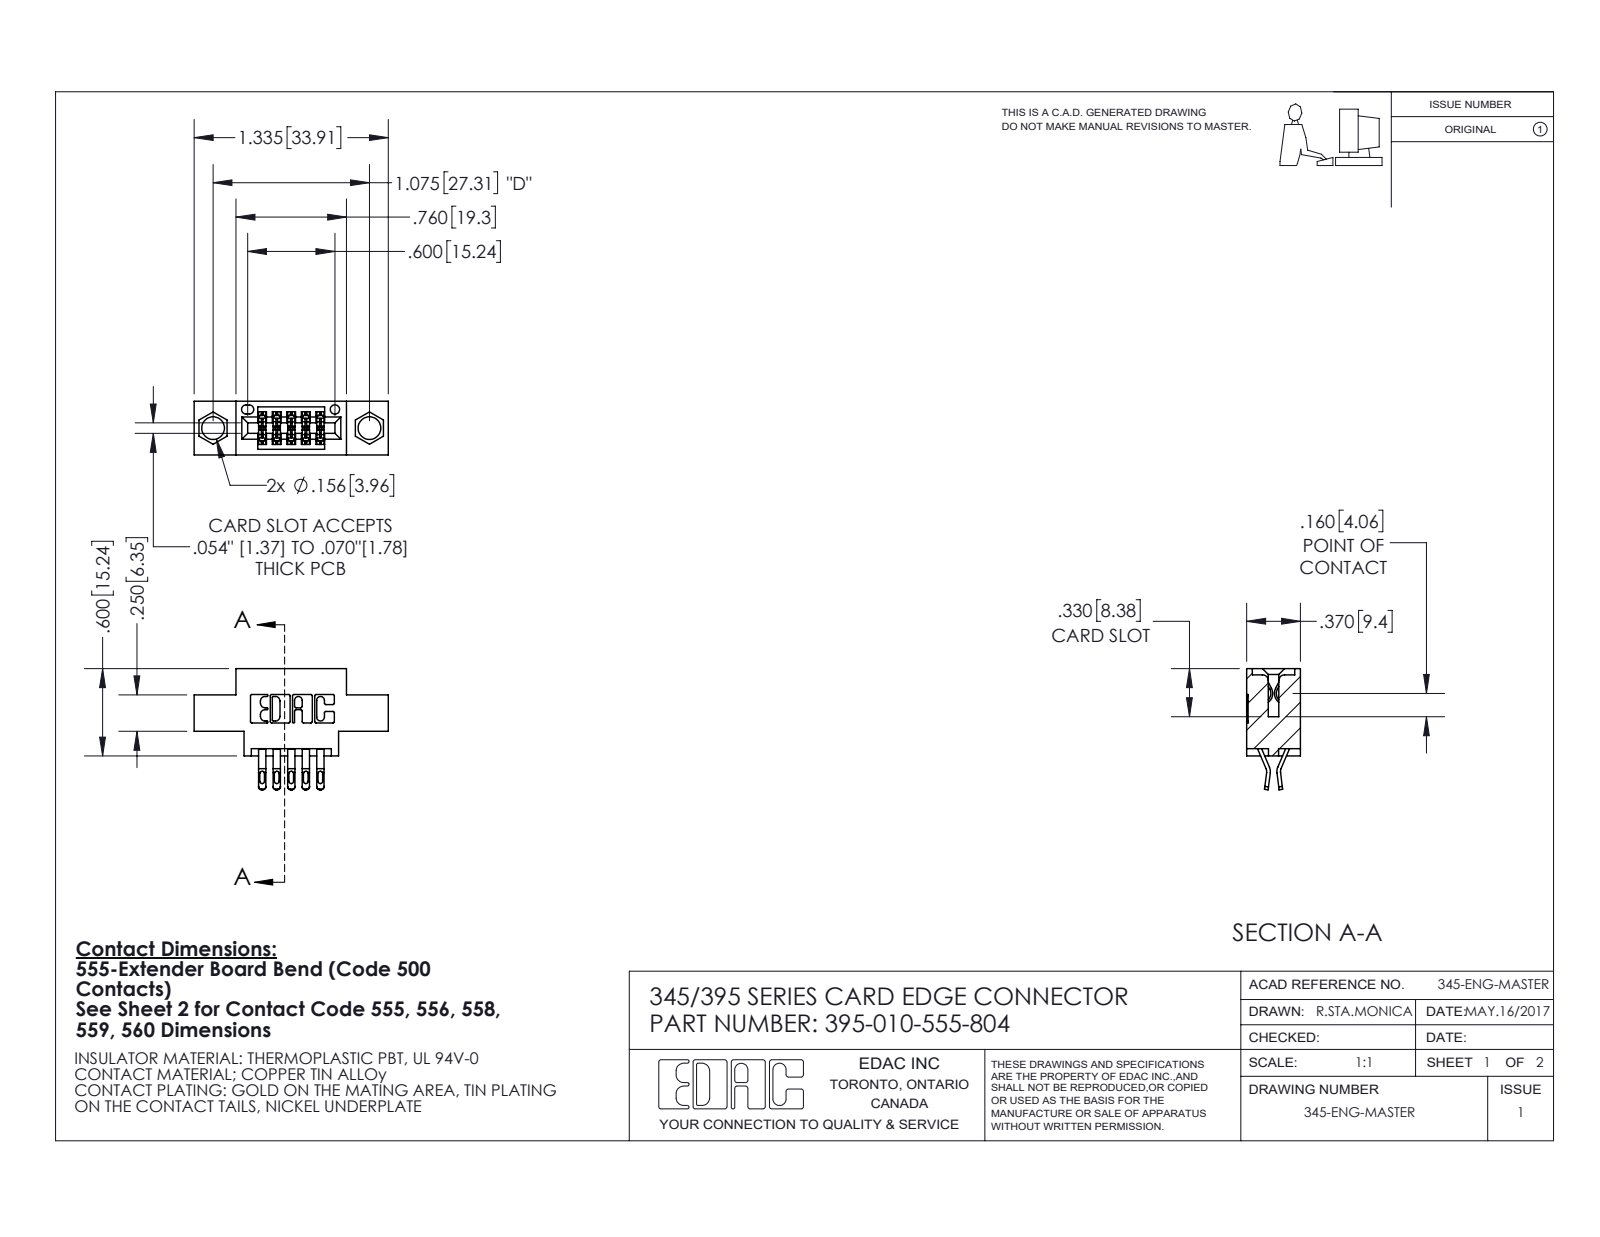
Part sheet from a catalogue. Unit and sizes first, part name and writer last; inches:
Units: inches
Overall size (bounding box): 1.335 × 0.832 × 0.37
Round holes (diameter × count): ⌀0.156 ×2, ⌀0.064 ×1
Partial cylindrical surfaces — rounded edges, fillets, slot ends (radius × count): R0.016 ×25, R0.01 ×22, R0.006 ×20, R0.02 ×20, R0.007 ×6, R0.031 ×6, R0.026 ×3, R0.01 ×2
Main face-to-face distances: 0.37, 0.2, 0.1, 0.072, 0.298, 0.25, 0.025, 0.15, 0.055, 0.098
Hole centre spacings: 0.27, 0.847, 1.075
Volume: 0.168 in³ · Surface area: 5.362 in²
Bodies: 11 solids, 704 faces (408 planar, 296 cylindrical, 0 other)
Part name (STEP PRODUCT): 395-010-555-804; 345 Part_0.170 Offset - 0.156 Dia-TI; 345-292-001_555 Tail
STEP written by: SolidWorks 2020 (CONFIG_CONTROL_DESIGN)
